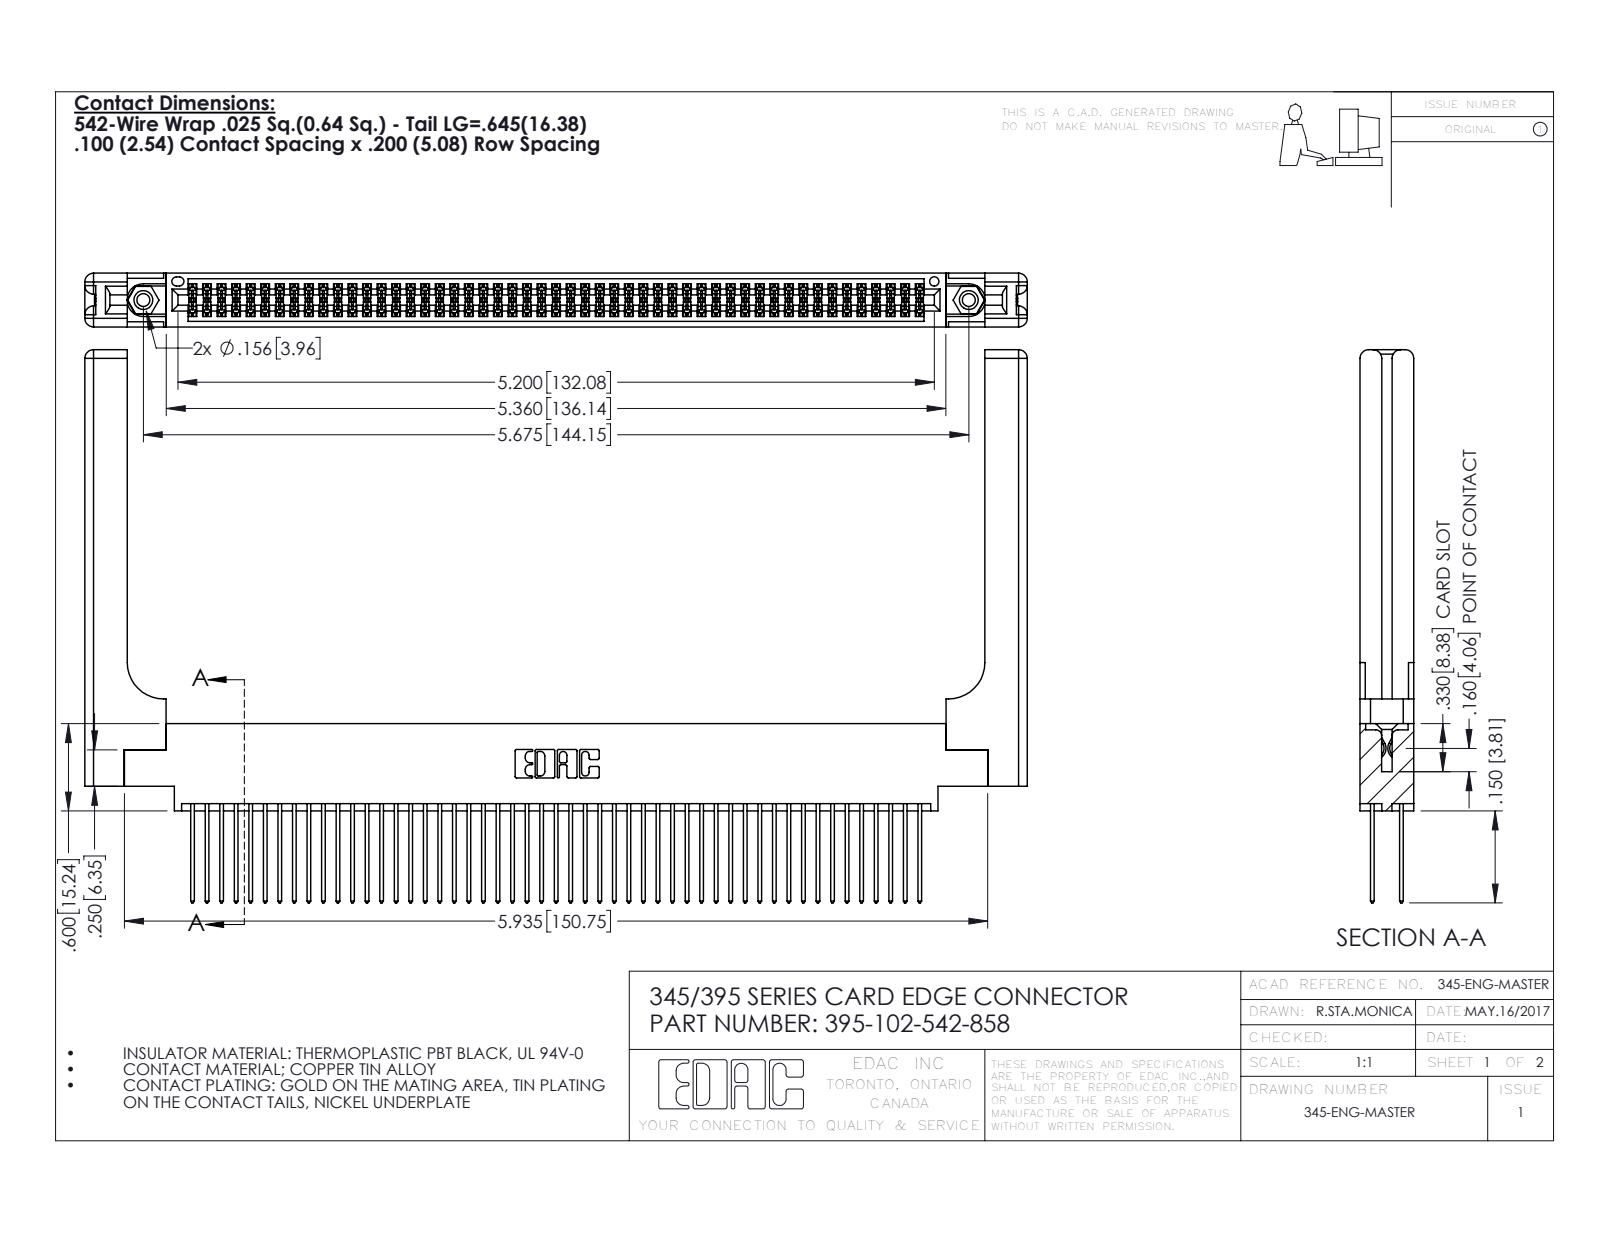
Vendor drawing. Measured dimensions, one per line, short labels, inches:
name: 395-102-542-858; 345-292-001_345-293-142; 345 Part_0.170 Offset - 0.156 Dia-TH; 345-220-058_345-220-058 (+1 more)
written by: SolidWorks 2016 (CONFIG_CONTROL_DESIGN)
unit: in
bodies: 107 solids, 5486 faces (3598 planar, 1828 cylindrical, 60 other)
size: 6.479 × 3.802 × 0.37
volume: 1.52 in³; area: 49.43 in²
holes: 2× ⌀0.089, 2× ⌀0.125, 2× ⌀0.156, 1× ⌀0.064
bosses: 2× ⌀0.155
rounds: 153× R0.006, 102× R0.01, 22× R0.01, 16× R0.06, 6× R0.007, 6× R0.031, 3× R0.026, 2× R0.014
face distances: 0.072, 0.298, 0.37, 0.098, 0.272, 0.025, 0.2, 0.225, 0.175, 0.148
hole spacings: 0.27, 5.439, 5.675
